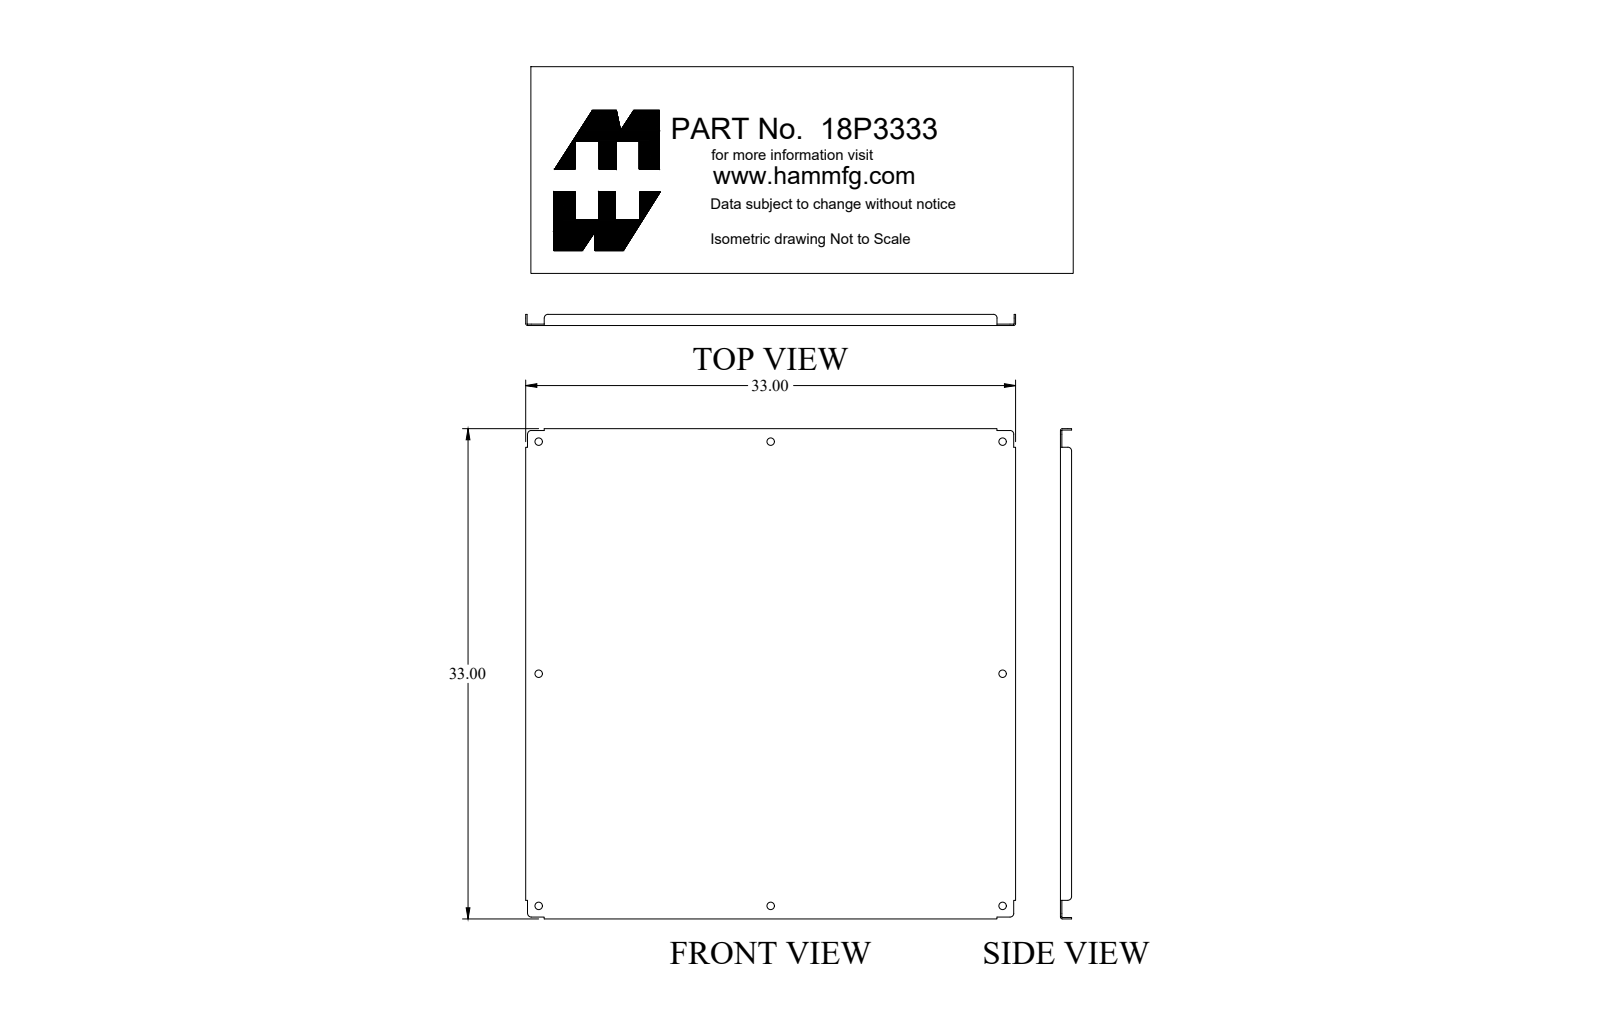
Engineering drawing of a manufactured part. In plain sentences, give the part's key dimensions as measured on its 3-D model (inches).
The part is named "18P3333_Default". Its 3-D file was written by "SolidWorks 2018 (CONFIG_CONTROL_DESIGN)". It is 1 solid with 66 faces: 30 planar, 36 cylindrical and 0 other. Overall it measures 33 by 33 by 0.75 inches. Its volume is 110.4 cubic inches and its surface area 2 338 square inches. Round holes: 8 of diameter 0.5. Partial cylindrical surfaces (rounded edges, fillets, slot ends): 8 of radius 0.25, 4 of radius 0.03, 4 of radius 0.125. The main face-to-face distances are 0.095, 32.905, 33, 32.81, 0.75, 0.655, 0.125, 32.875, 0.03, 32.78. The hole center spacings are 15.625, 34.939, 31.25, 22.097, 44.195.
